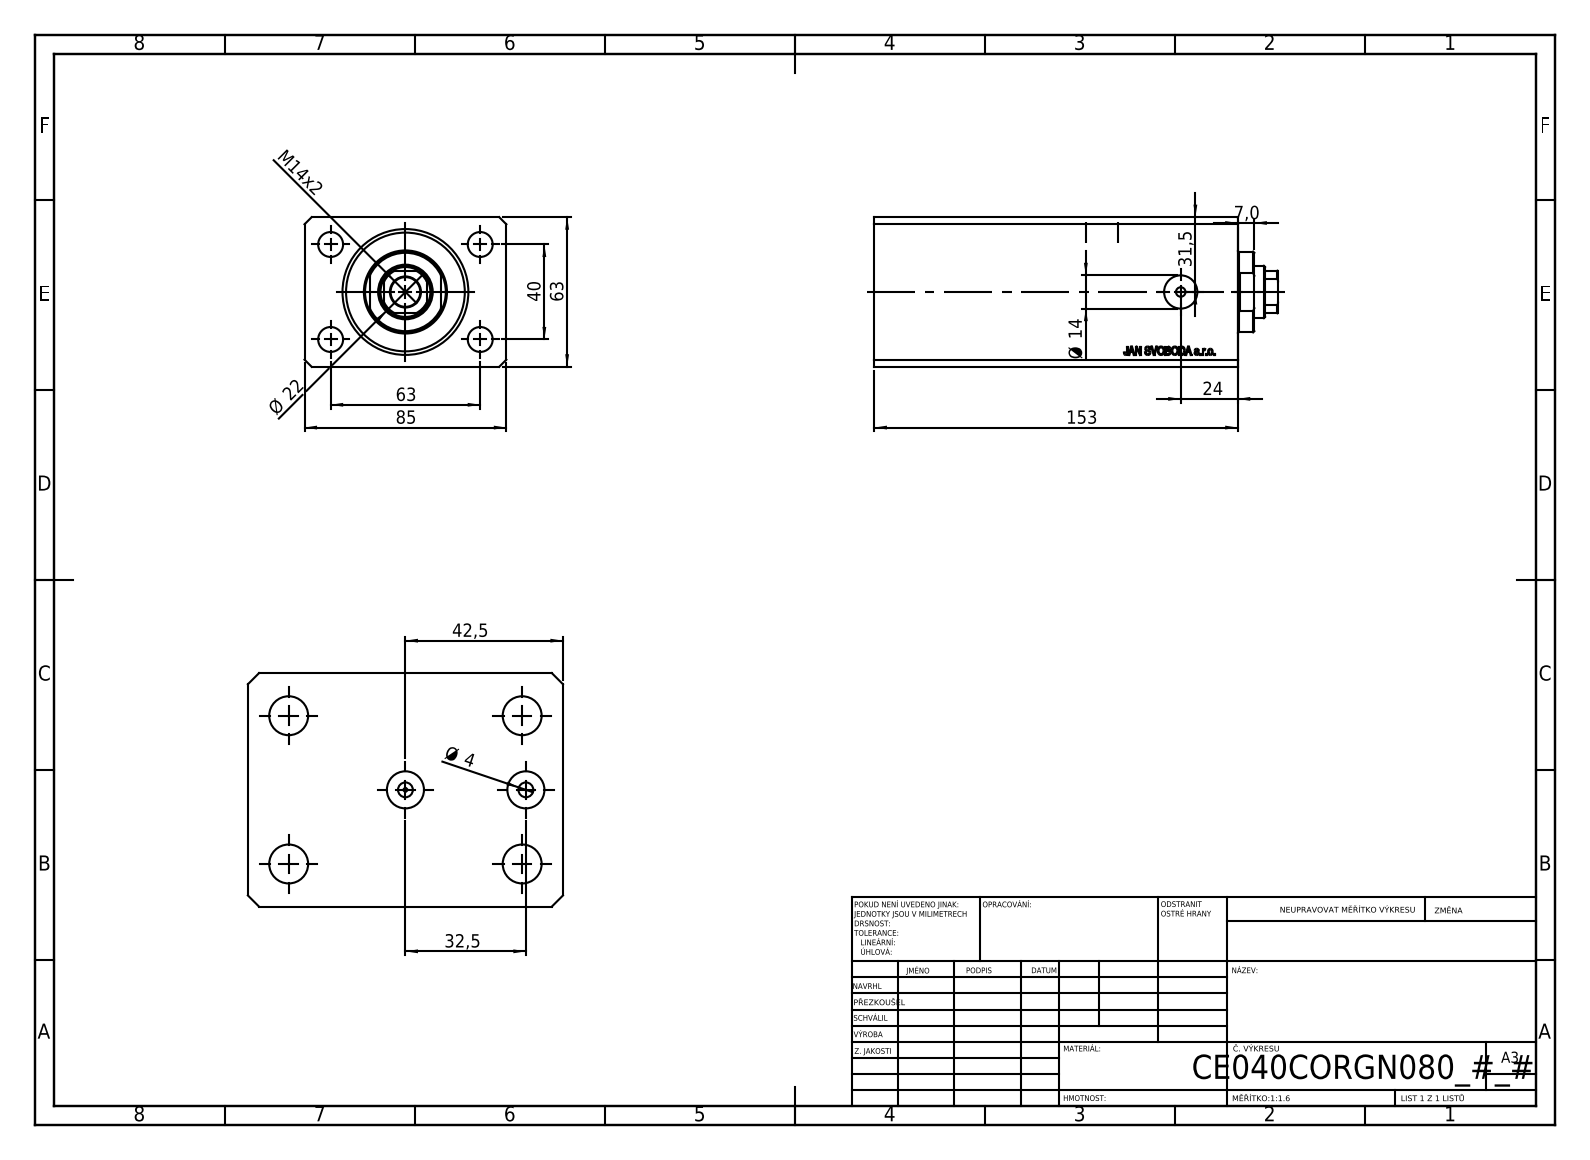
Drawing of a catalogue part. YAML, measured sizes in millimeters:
part_name: "V250CE_C_Body; V250CE_C_VCP; V250CE_VC_C"
step_written_by: "SolidWorks 2019 (CONFIG_CONTROL_DESIGN)"
units: millimeters
bodies: {solids: 3, faces: 868, planar: 428, cylindrical: 46, other: 394}
overall_size: [170, 85, 63]
volume: 696416
surface_area: 121092
round_holes:
  - {diameter: 4, count: 4}
  - {diameter: 10.5, count: 4}
  - {diameter: 10, count: 2}
  - {diameter: 14, count: 2}
  - {diameter: 1.25, count: 1}
  - {diameter: 12.5, count: 1}
  - {diameter: 22, count: 1}
  - {diameter: 40, count: 1}
  - {diameter: 53, count: 1}
round_bosses_or_shafts:
  - {diameter: 34, count: 1}
partial_cylinders:
  - {radius: 10.5, count: 1}
face_to_face_distances: [63, 85, 153, 17, 136, 11.4, 124.6, 141.6, 100.4, 80]
hole_center_spacings: [37.31, 20.02, 40, 63, 67.05, 74.63, 32.5, 105]
